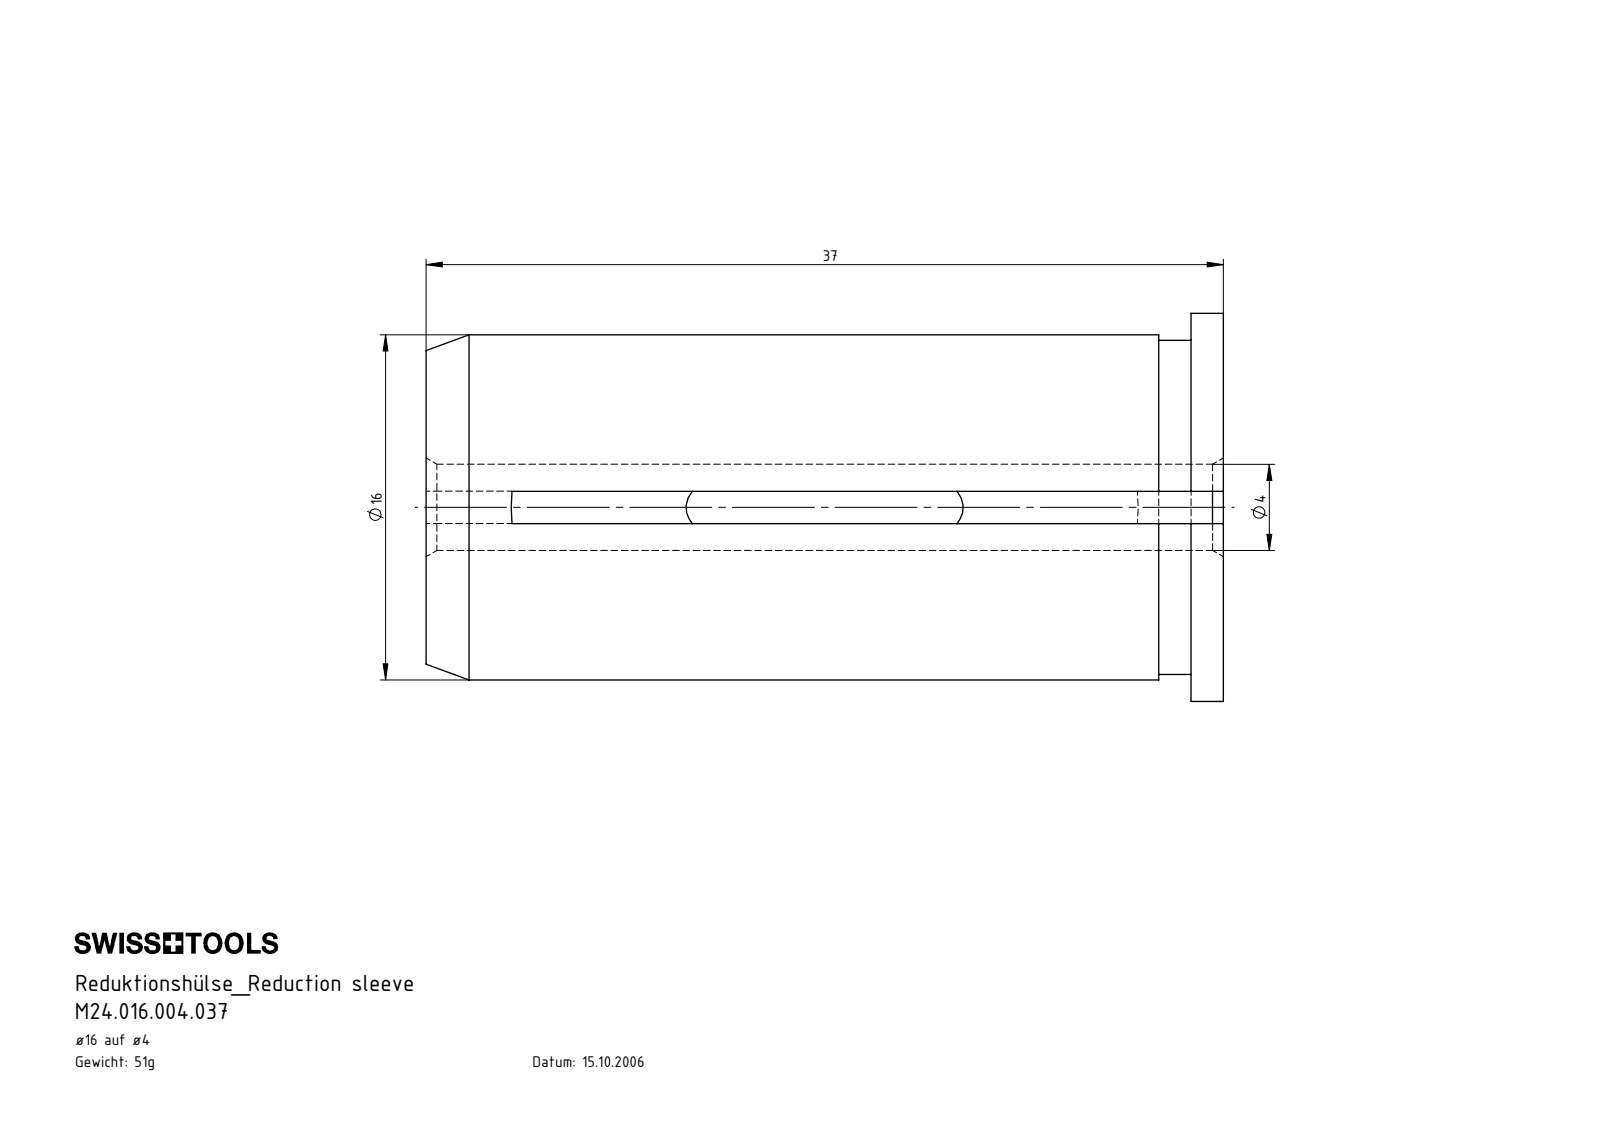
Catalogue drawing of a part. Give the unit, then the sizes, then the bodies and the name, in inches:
Units: inches
Overall size (bounding box): 1.457 × 0.709 × 0.707
Round holes (diameter × count): ⌀0.157 ×1
Round bosses / shafts (diameter × count): ⌀0.709 ×1, ⌀0.63 ×1, ⌀0.61 ×1
Partial cylindrical surfaces — rounded edges, fillets, slot ends (radius × count): R1.24 ×2
Main face-to-face distances: 0.059, 1.457, 1.398, 1.339, 0.118
Volume: 0.395 in³ · Surface area: 5.199 in²
Bodies: 1 solid, 17 faces (8 planar, 6 cylindrical, 3 other)
Part name (STEP PRODUCT): U04.U16.001.037
STEP written by: SolidWorks 2017 (AUTOMOTIVE_DESIGN)
